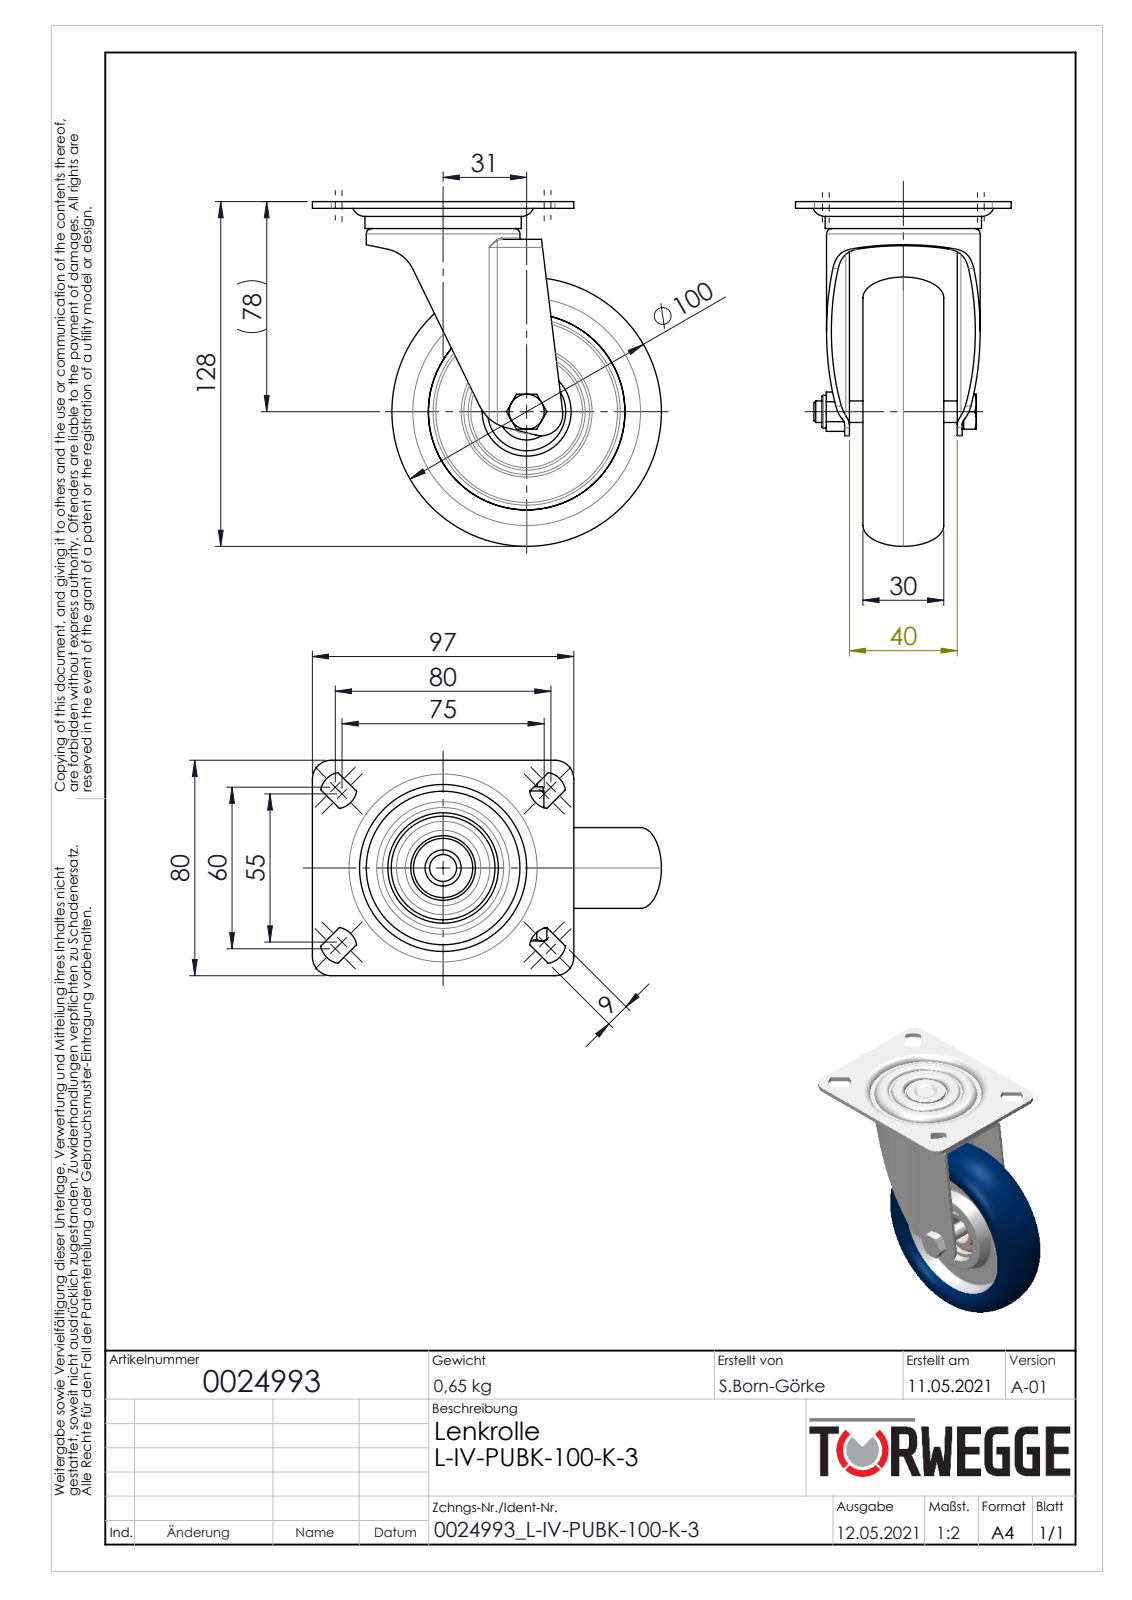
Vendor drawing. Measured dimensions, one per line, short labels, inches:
name: 0024993
written by: SolidWorks 2020 (AUTOMOTIVE_DESIGN)
unit: in
bodies: 8 solids, 264 faces (76 planar, 68 cylindrical, 120 other)
size: 5.098 × 5.039 × 3.15
volume: 12.47 in³; area: 151.4 in²
holes: 1× ⌀0.262, 1× ⌀0.315, 1× ⌀0.327, 1× ⌀0.394, 1× ⌀0.945, 1× ⌀1.299, 1× ⌀1.378, 1× ⌀2.102
bosses: 1× ⌀2.283, 1× ⌀2.244, 1× ⌀1.142, 1× ⌀0.866, 1× ⌀0.591, 1× ⌀0.512, 1× ⌀0.48
rounds: 8× R0.318, 4× R0.276, 2× R0.047, 2× R0.118, 2× R0.197, 2× R0.268, 1× R0.315, 1× R0.523
face distances: 0.071, 0.295, 0.098, 0.394, 0.669, 0.906, 0.74, 0.976, 1.646, 0.366
